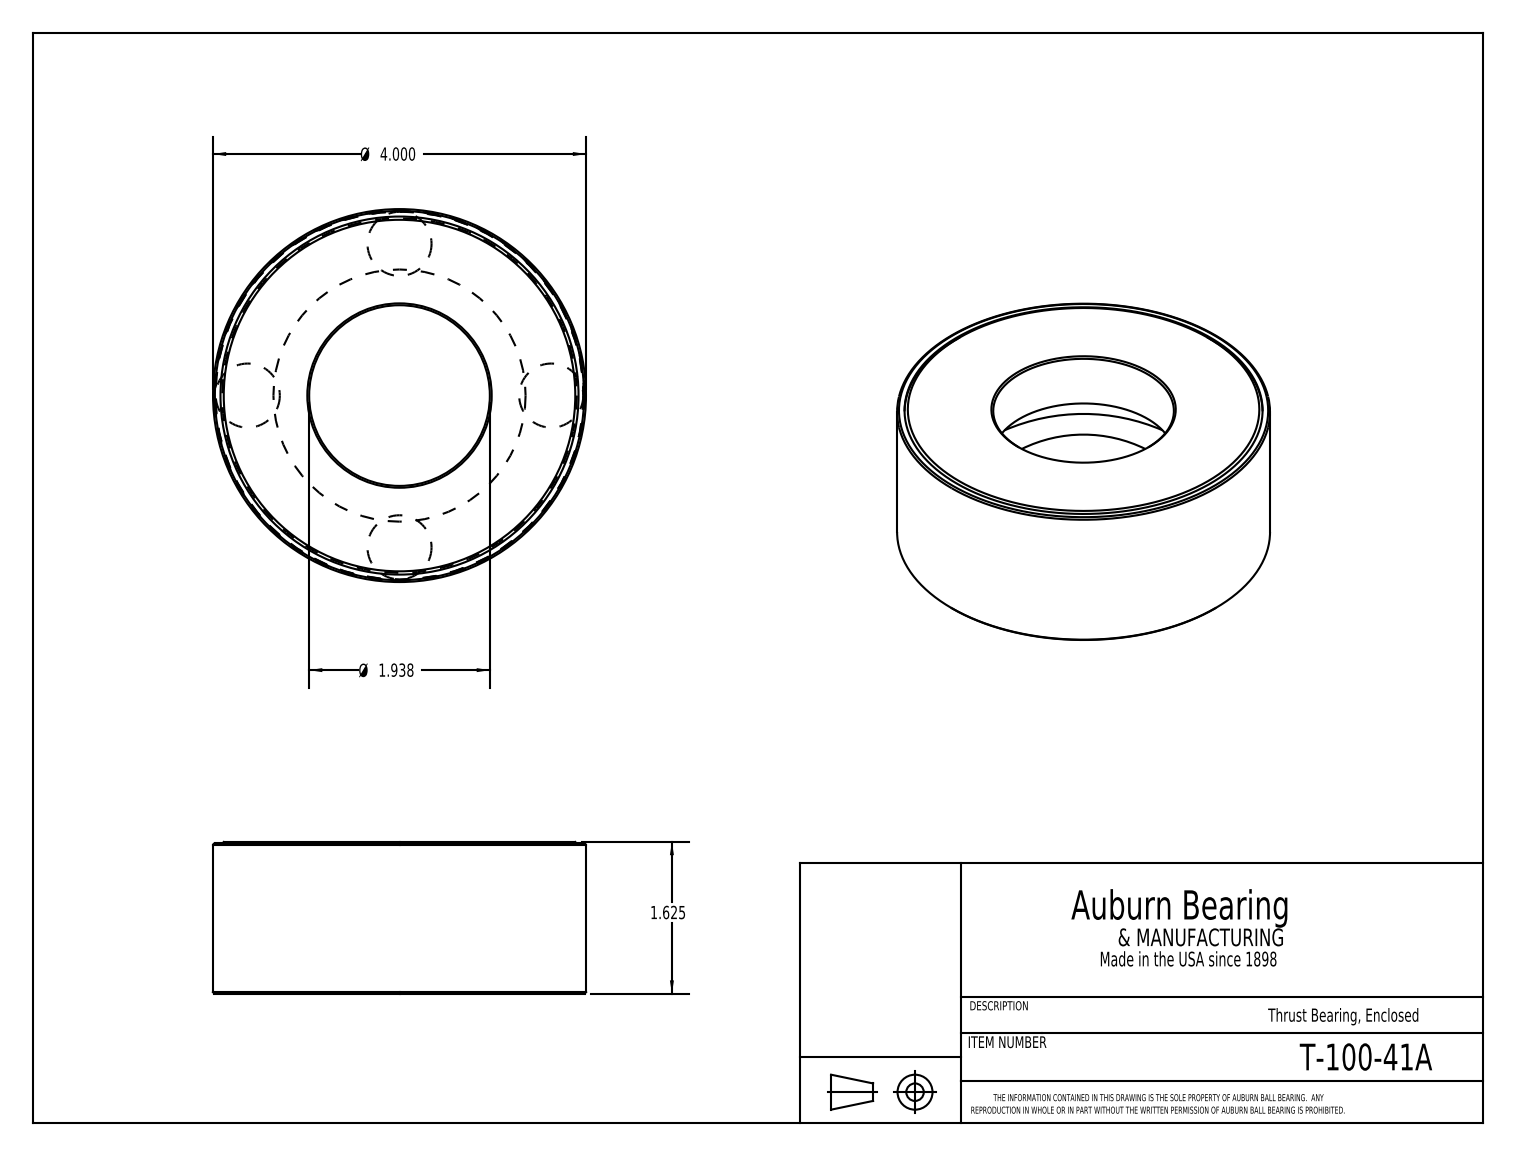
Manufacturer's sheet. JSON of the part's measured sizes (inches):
{"part_name": "T-100-41A", "step_written_by": "SolidWorks 2016 (CONFIG_CONTROL_DESIGN)", "units": "inches", "bodies": {"solids": 6, "faces": 28, "planar": 9, "cylindrical": 7, "other": 12}, "overall_size": [4, 4, 1.625], "volume_in3": 11.27, "surface_area_in2": 93.68, "round_holes": [[1.937, 1], [3.84, 1], [3.96, 1]], "round_bosses_or_shafts": [[4, 1], [3.946, 1]], "face_to_face_distances": [1.625, 0.606, 1.019, 1.019, 0.413, 0.606, 1.59, 1.61, 0.984, 1.004]}
